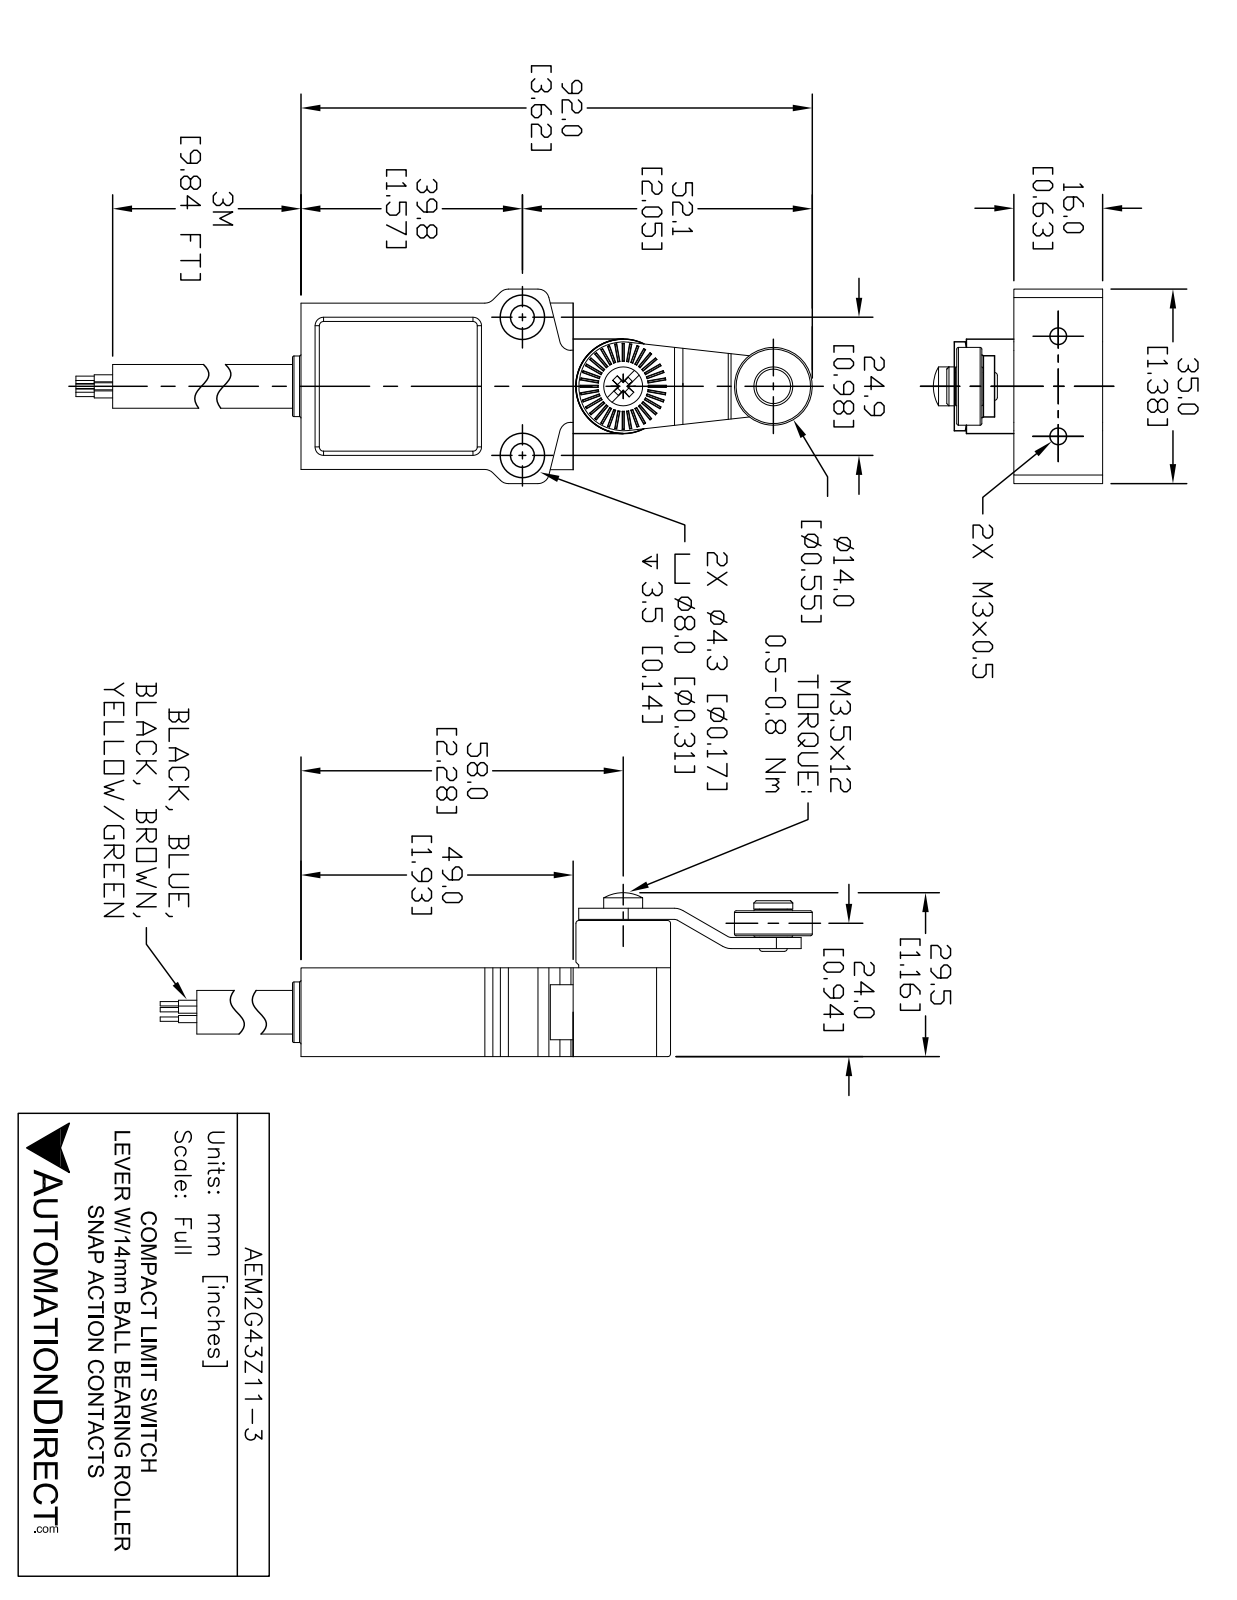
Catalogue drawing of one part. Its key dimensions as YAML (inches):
part_name: "AEM2G43Z11-3_Default"
step_written_by: "SolidWorks 2021 (CONFIG_CONTROL_DESIGN)"
units: inches
bodies: {solids: 4, faces: 308, planar: 248, cylindrical: 49, other: 11}
overall_size: [4.124, 1.378, 1.184]
volume: 1.835
surface_area: 16.56
round_holes:
  - {diameter: 0.118, count: 2}
  - {diameter: 0.173, count: 2}
  - {diameter: 0.323, count: 2}
  - {diameter: 0.197, count: 1}
round_bosses_or_shafts:
  - {diameter: 0.276, count: 2}
  - {diameter: 0.622, count: 1}
  - {diameter: 0.55, count: 1}
  - {diameter: 0.28, count: 1}
  - {diameter: 0.202, count: 1}
  - {diameter: 0.143, count: 1}
partial_cylinders:
  - {radius: 0.079, count: 8}
  - {radius: 0.06, count: 2}
  - {radius: 0.14, count: 1}
  - {radius: 0.192, count: 1}
  - {radius: 0.256, count: 1}
  - {radius: 0.313, count: 1}
face_to_face_distances: [0.63, 1.181, 1.929, 0.354, 0.08, 0.984, 0.121, 0.28, 0.902, 0.472]
hole_center_spacings: [0.863, 0.748, 0.984]
